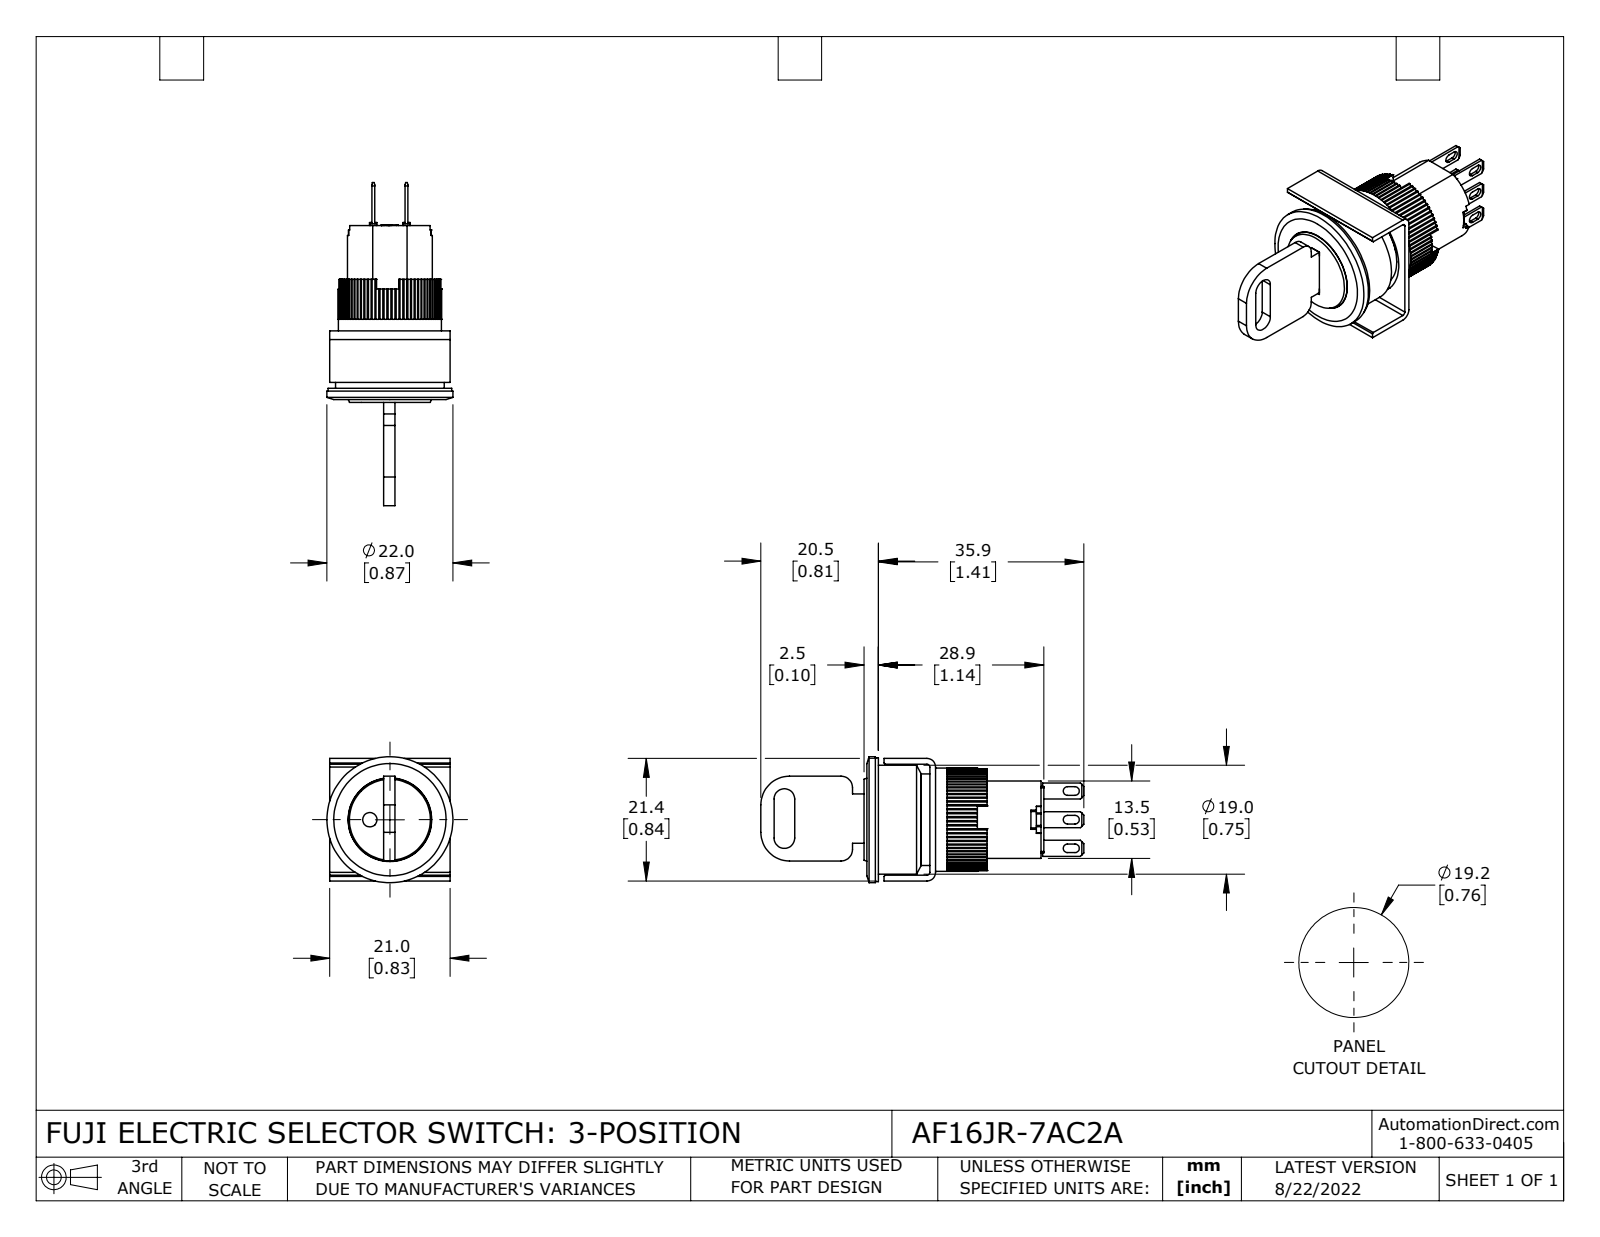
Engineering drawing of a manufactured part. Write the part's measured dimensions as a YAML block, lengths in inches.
part_name: "AF16JR-7AC2A"
step_written_by: "SolidWorks 2021 (CONFIG_CONTROL_DESIGN)"
units: inches
bodies: {solids: 13, faces: 707, planar: 518, cylindrical: 183, other: 6}
overall_size: [2.22, 0.866, 0.866]
volume: 0.495
surface_area: 11.24
round_holes:
  - {diameter: 0.039, count: 1}
  - {diameter: 0.098, count: 1}
  - {diameter: 0.575, count: 1}
  - {diameter: 0.709, count: 1}
  - {diameter: 0.748, count: 1}
round_bosses_or_shafts:
  - {diameter: 0.866, count: 1}
  - {diameter: 0.85, count: 1}
  - {diameter: 0.63, count: 1}
  - {diameter: 0.583, count: 1}
  - {diameter: 0.571, count: 1}
partial_cylinders:
  - {radius: 0.01, count: 80}
  - {radius: 0.008, count: 12}
  - {radius: 0.03, count: 6}
  - {radius: 0.02, count: 2}
  - {radius: 0.059, count: 2}
  - {radius: 0.071, count: 2}
  - {radius: 0.079, count: 2}
  - {radius: 0.197, count: 2}
face_to_face_distances: [0.079, 0.039, 0.02, 0.374, 0.177, 0.098, 0.394, 0.803, 0.059, 0.764]
hole_center_spacings: [0.138]
